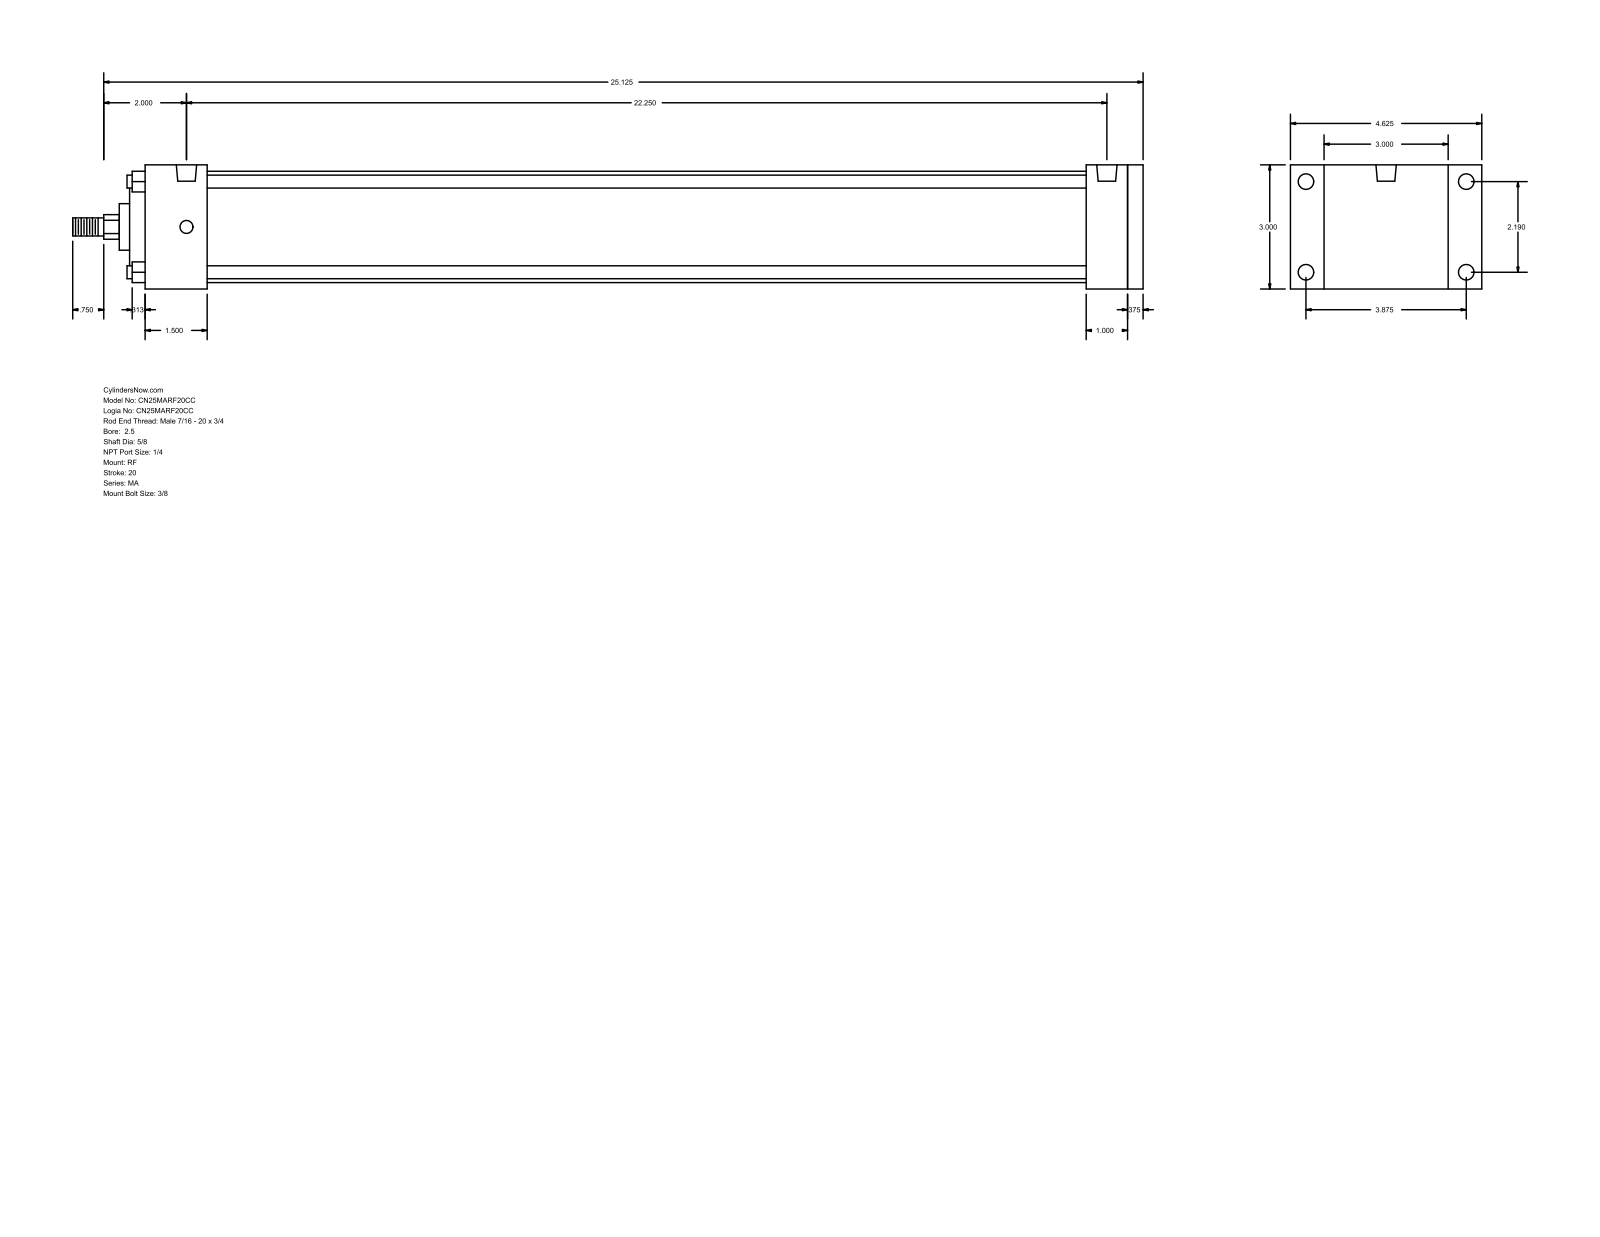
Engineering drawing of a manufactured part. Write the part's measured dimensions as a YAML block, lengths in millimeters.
part_name: "MA_RF__0250_0.625"
step_written_by: "GSSL Pune (CONFIG_CONTROL_DESIGN)"
units: millimeters
bodies: {solids: 0, faces: 94, planar: 65, cylindrical: 29, other: 0}
overall_size: [657.23, 117.47, 76.2]
round_holes:
  - {diameter: 7.94, count: 4}
  - {diameter: 9.53, count: 4}
  - {diameter: 12.49, count: 2}
round_bosses_or_shafts:
  - {diameter: 7.94, count: 4}
  - {diameter: 68.33, count: 1}
  - {diameter: 50.8, count: 1}
  - {diameter: 28.57, count: 1}
  - {diameter: 15.88, count: 1}
  - {diameter: 11.11, count: 1}
partial_cylinders:
  - {radius: 7.54, count: 1}
face_to_face_distances: [76.2, 612.77, 9.52, 603.25, 25.4, 38.1, 577.85, 539.75, 565.15, 574.67]
hole_center_spacings: [55.62, 98.42, 113.05, 565.15]
